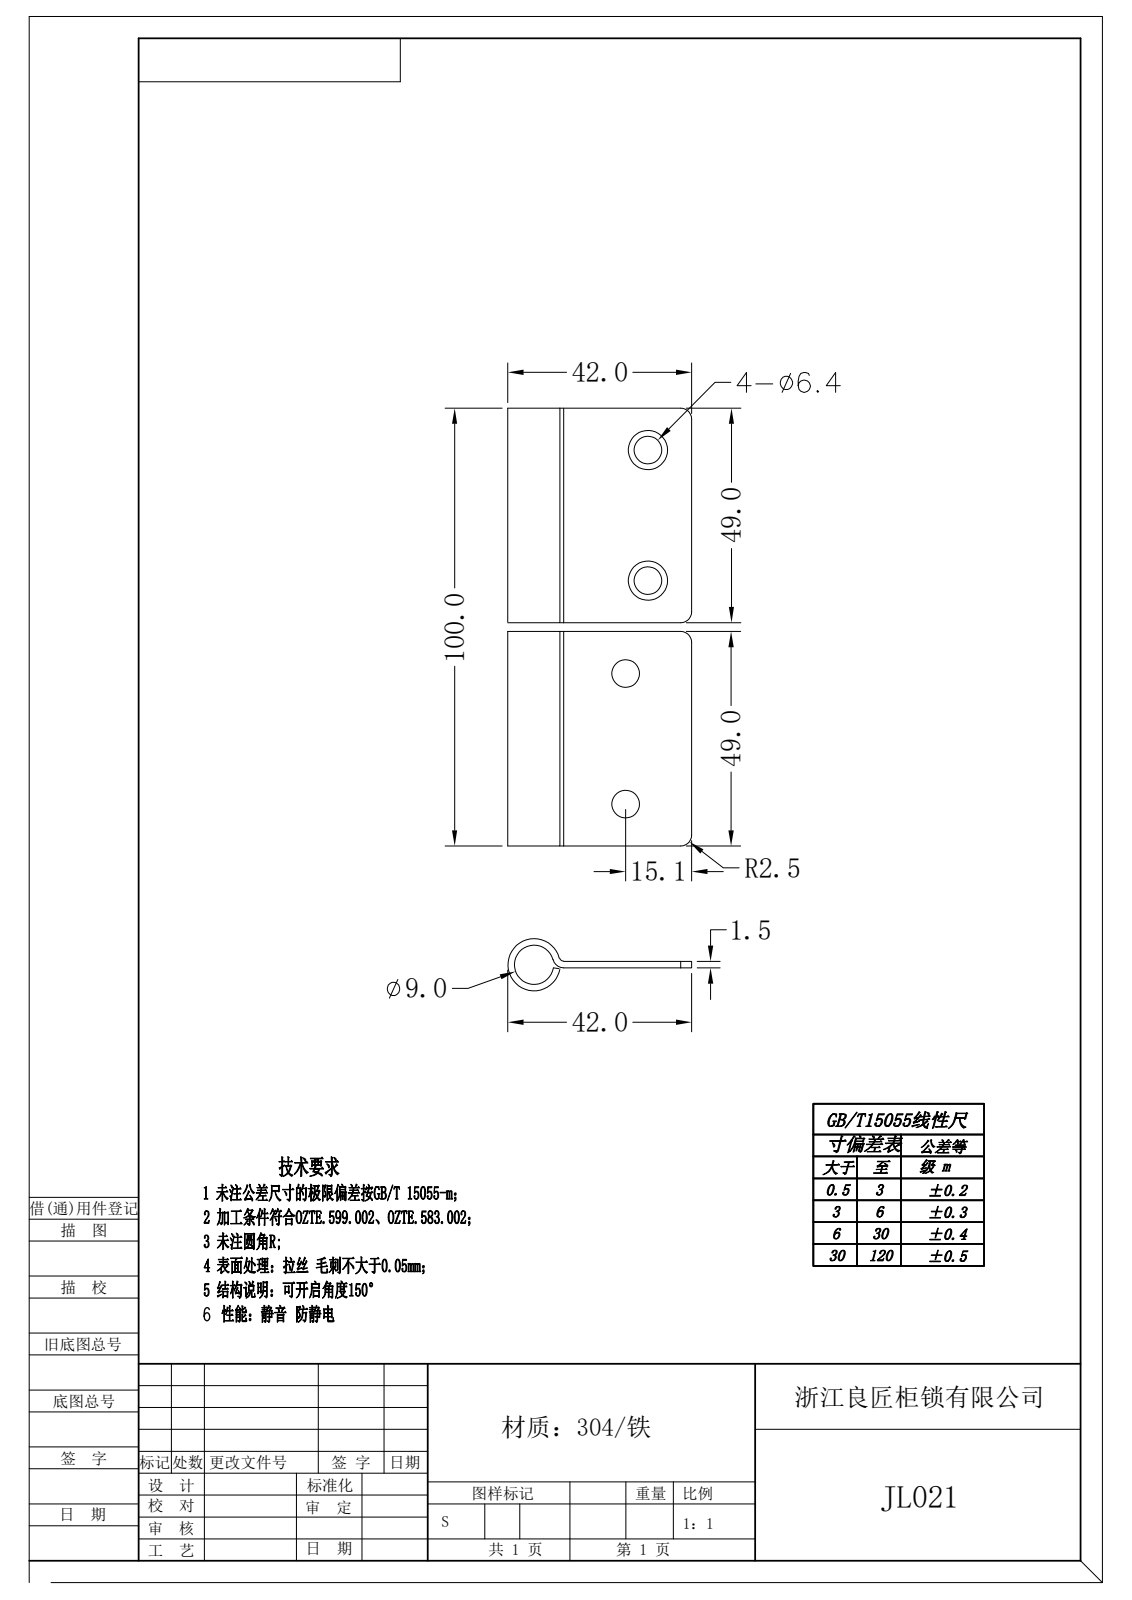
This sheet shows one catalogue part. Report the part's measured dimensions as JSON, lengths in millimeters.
{"step_written_by": "Rhino 8.5 (CONFIG_CONTROL_DESIGN)", "units": "millimeters", "bodies": {"solids": 4, "faces": 44, "planar": 16, "cylindrical": 16, "other": 12}, "overall_size": [100, 72, 12], "volume_mm3": 15007, "surface_area_mm2": 15806, "round_holes": [[9, 1]], "round_bosses_or_shafts": [[12, 1], [8.7, 1]], "partial_cylinders_radius": [[2.5, 4], [1, 2], [2.5, 2]], "face_to_face_distances": [1.5, 49.15, 50.85, 49, 51, 1.85, 100, 1.7, 2, 72]}
